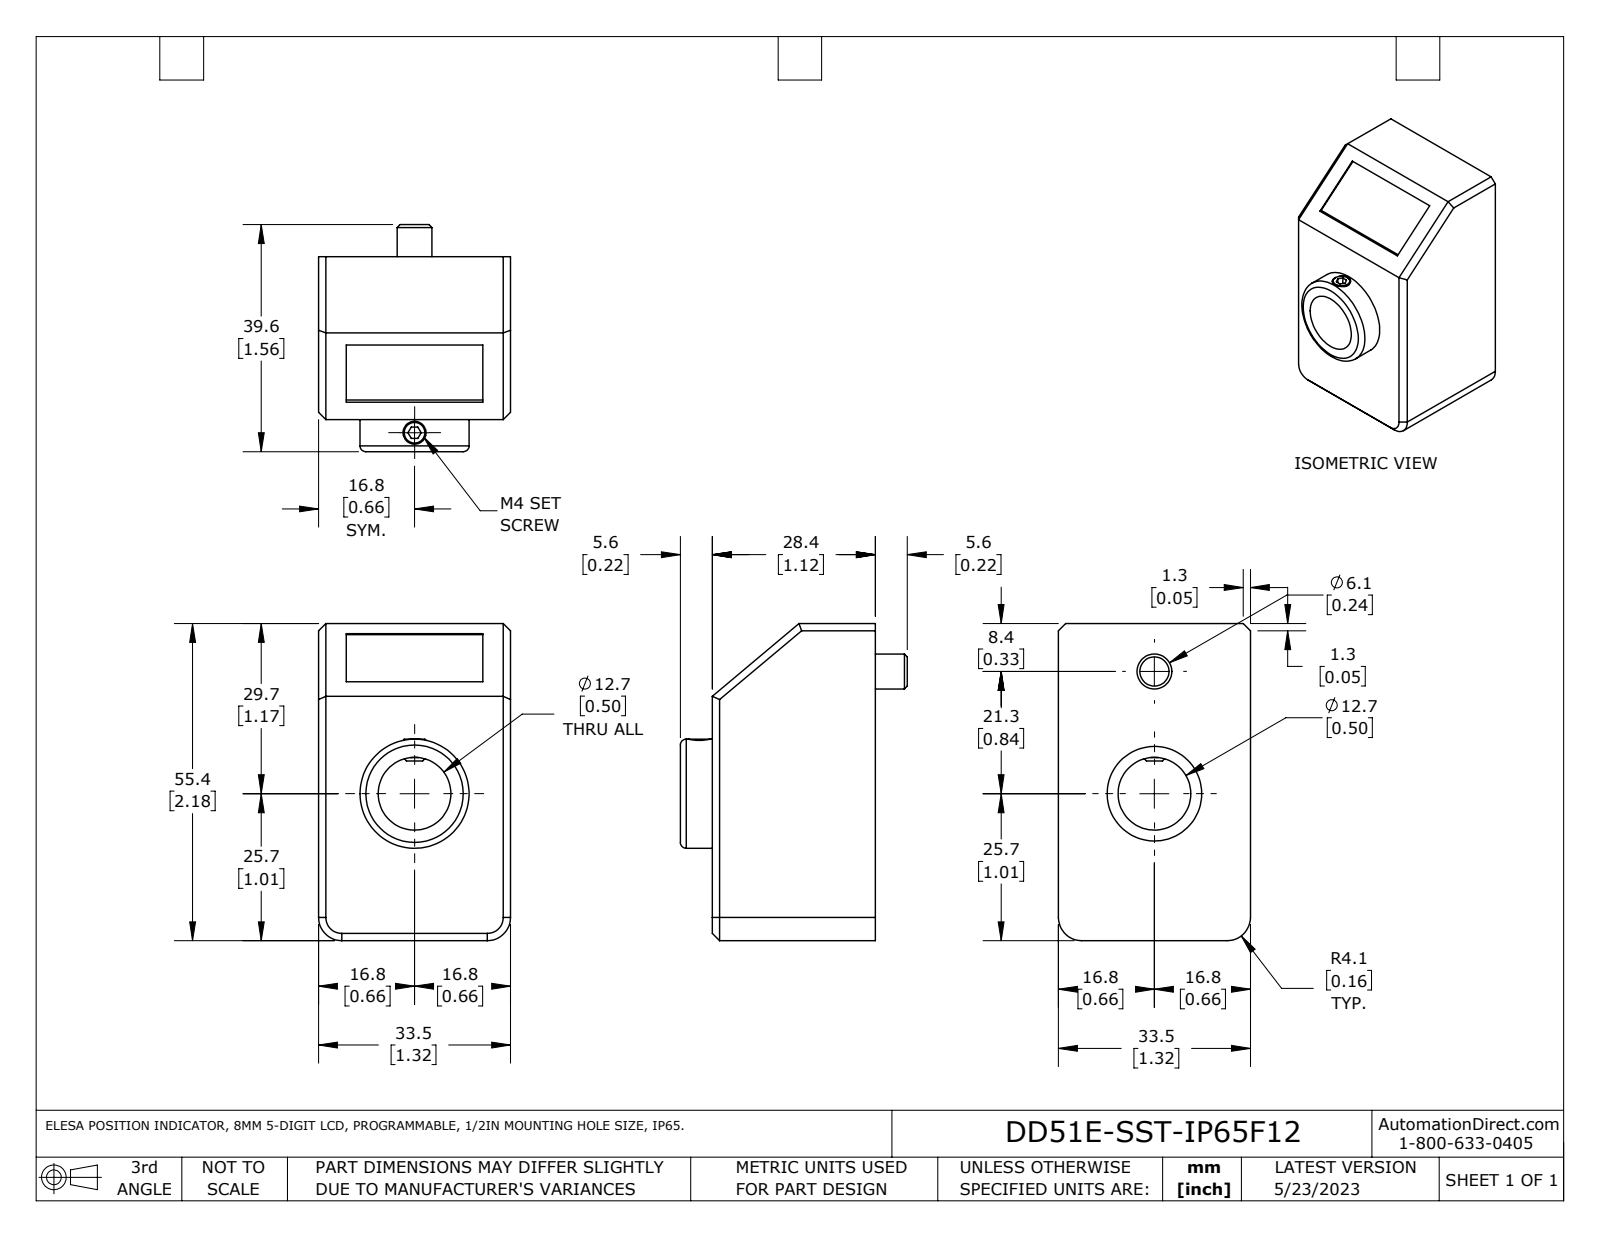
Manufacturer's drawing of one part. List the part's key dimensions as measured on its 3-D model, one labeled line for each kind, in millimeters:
Part name (STEP PRODUCT): DD51E-SST-IP65F12
STEP written by: SolidWorks 2021 (AUTOMOTIVE_DESIGN)
Units: millimetres
Bodies: 1 solid, 55 faces (37 planar, 12 cylindrical, 6 other)
Overall size (bounding box): 55.4 × 39.6 × 33.5
Volume: 45 380 mm³ · Surface area: 10 410 mm²
Round holes (diameter × count): ⌀4 ×1, ⌀12.7 ×1, ⌀16.5 ×1
Round bosses / shafts (diameter × count): ⌀19.1 ×1, ⌀6.1 ×1
Partial cylindrical surfaces — rounded edges, fillets, slot ends (radius × count): R4.1 ×2
Main face-to-face distances: 33.5, 28.4, 55.4, 0.4, 13.2, 45.2, 10.2, 15.2, 5.6, 34
